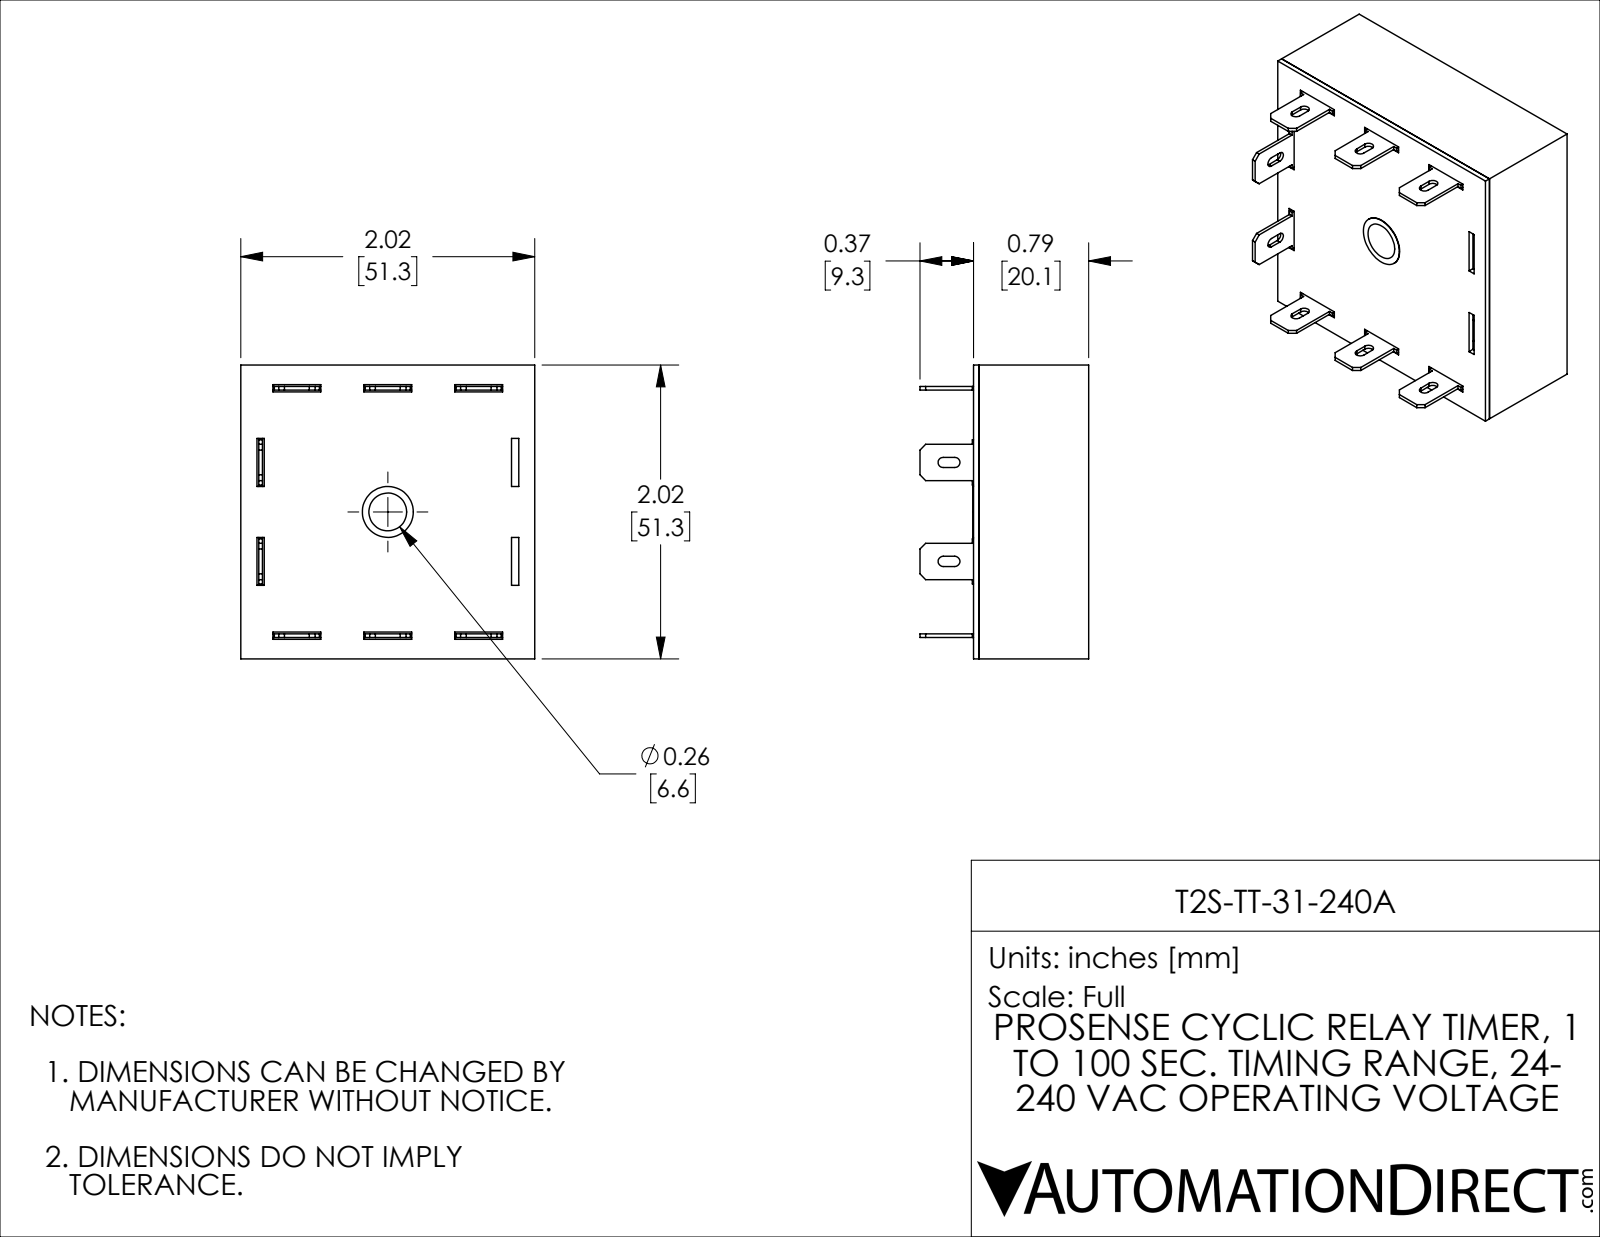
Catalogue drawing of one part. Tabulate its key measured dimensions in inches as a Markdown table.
| quantity | value |
| --- | --- |
| part name | T2S-TT-31-240A |
| STEP written by | SolidWorks 2021 (CONFIG_CONTROL_DESIGN) |
| units | inches |
| bodies | 10 solids, 256 faces (234 planar, 20 cylindrical, 2 other) |
| overall size | 2.02 × 2.02 × 1.16 |
| volume | 0.674 in³ |
| surface area | 35.37 in² |
| round holes (diameter × count) | 0.35 × 1 |
| partial cylindrical surfaces (radius × count) | 0.035 × 10 |
| main face-to-face distances | 0.045, 1.975, 0.754, 0.792, 0.038, 0.709, 0.747, 2.02, 1.93, 0.147 |
